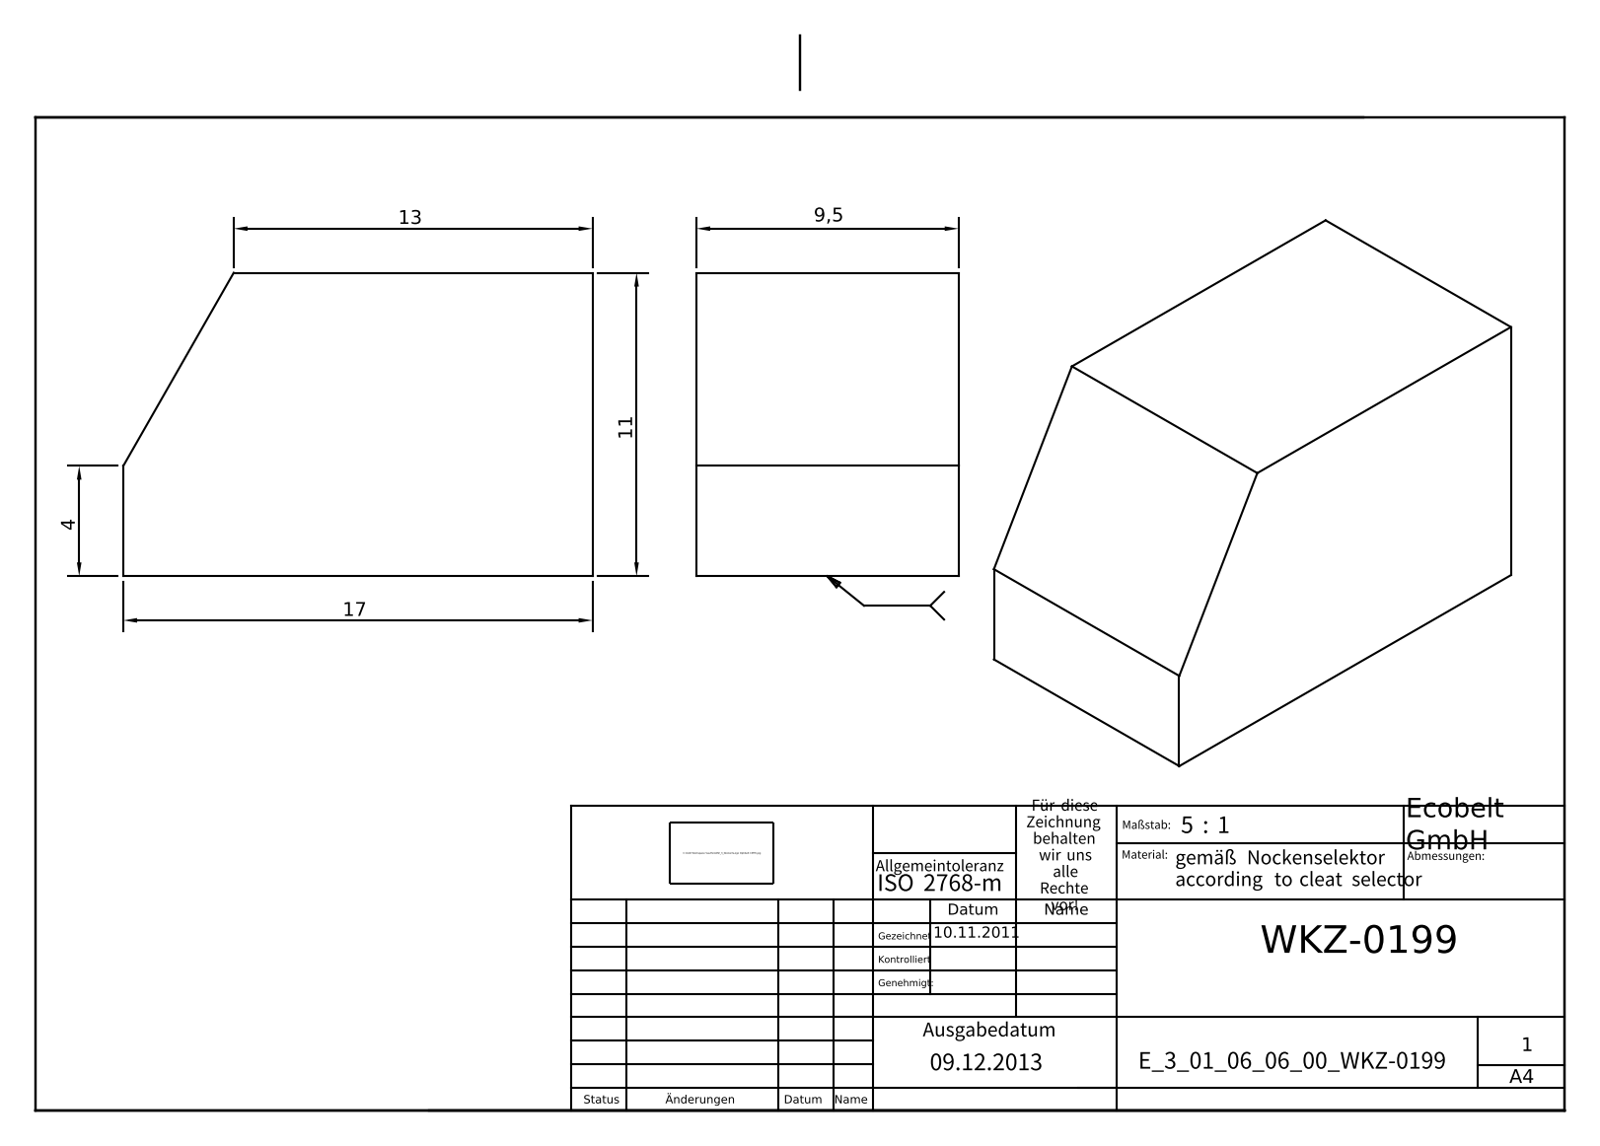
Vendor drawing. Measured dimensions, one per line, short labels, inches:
name: E_3_01_06_06_00_WKZ-0199
written by: Autodesk Inventor 2025 (AUTOMOTIVE_DESIGN)
unit: in
bodies: 1 solid, 7 faces (7 planar, 0 cylindrical, 0 other)
size: 0.669 × 0.433 × 0.374
volume: 0.1 in³; area: 1.32 in²
face distances: 0.374, 0.433, 0.669
